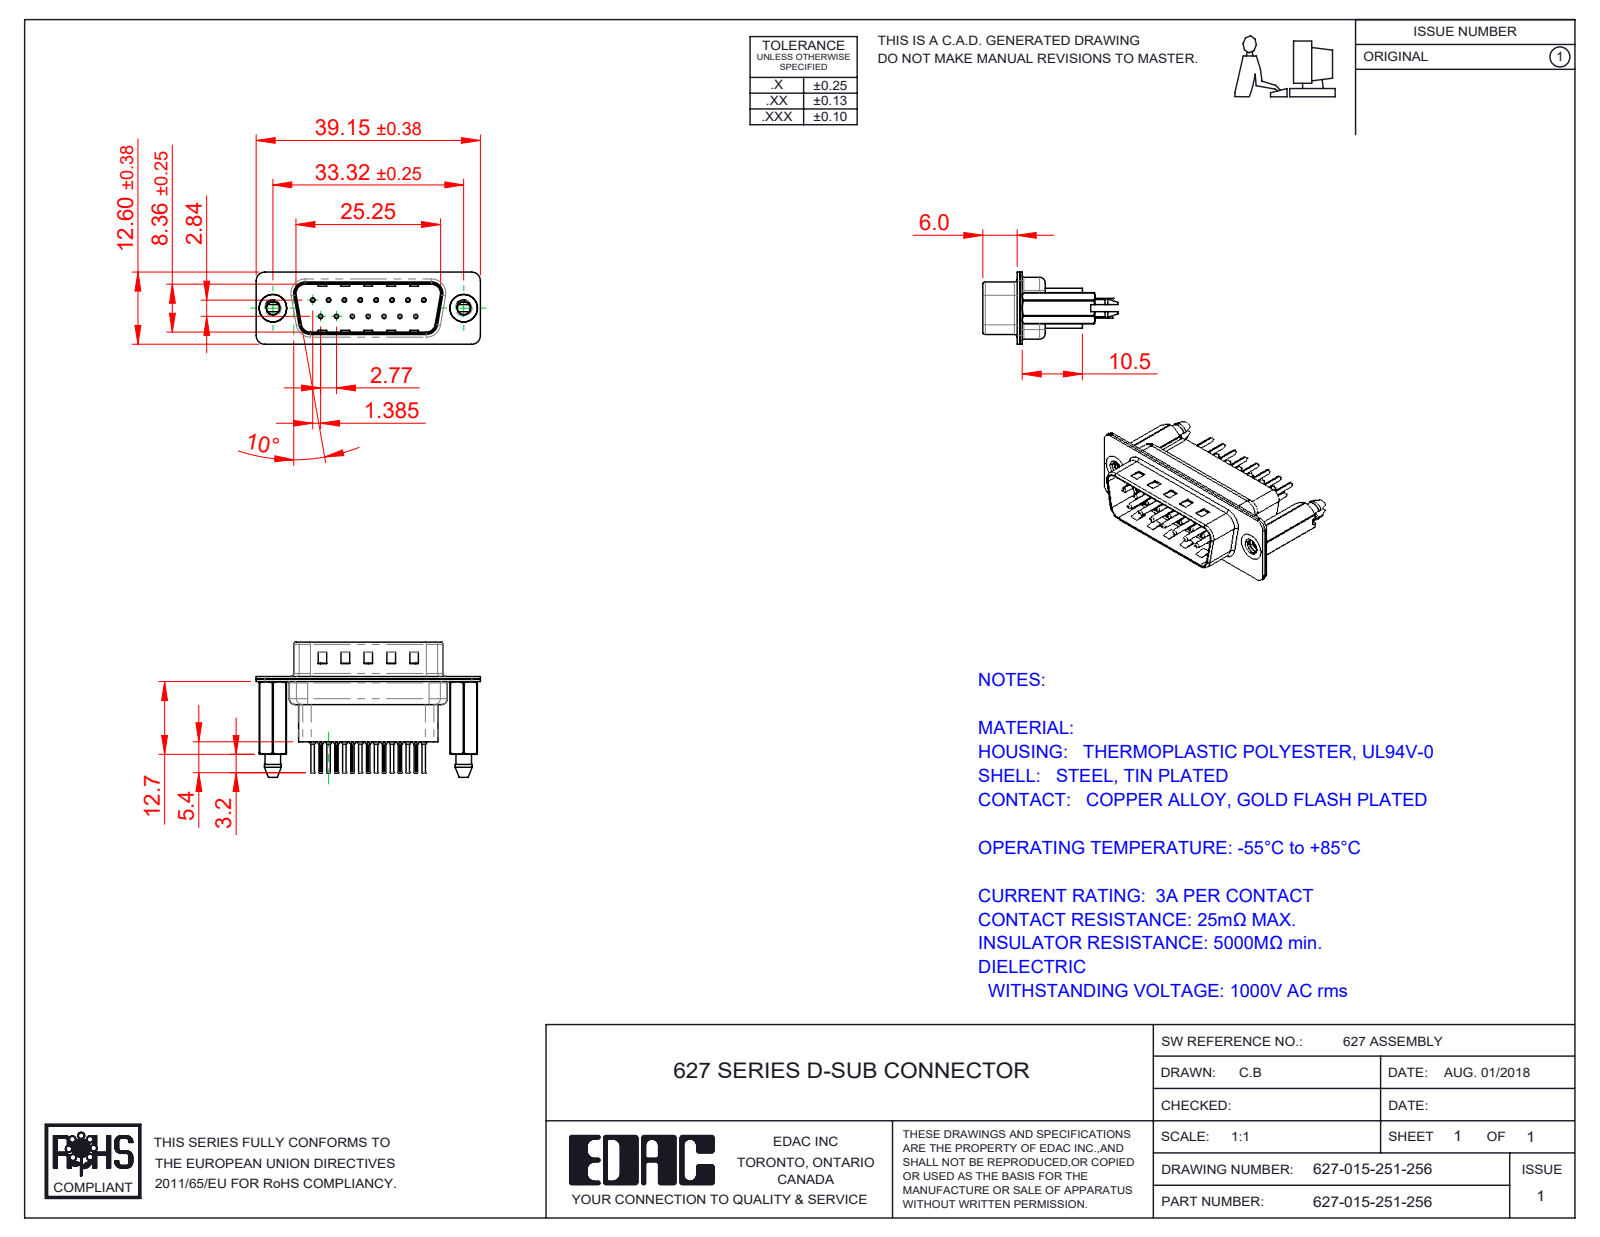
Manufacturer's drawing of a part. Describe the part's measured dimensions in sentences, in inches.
The part is named "627 Contact Row 1_41; 627 Shell Rear_15 Contacts; 627 Shell Front_15 Contacts; 627 Contact Row 2_41 (+3 more)". Its 3-D file was written by "SolidWorks 2020 (CONFIG_CONTROL_DESIGN)". It is 20 solids with 1918 faces: 531 planar, 754 cylindrical and 633 other. Overall it measures 1.541 by 0.929 by 0.496 inches. Its volume is 0.174 cubic inches and its surface area 11.42 square inches. Round holes: 15 of diameter 0.008, 15 of diameter 0.014, 15 of diameter 0.043, 15 of diameter 0.063, 2 of diameter 0.089, 2 of diameter 0.157, 2 of diameter 0.189. Round bosses or shafts: 15 of diameter 0.079, 15 of diameter 0.059, 15 of diameter 0.03, 15 of diameter 0.024, 2 of diameter 0.193. Partial cylindrical surfaces (rounded edges, fillets, slot ends): 30 of radius 0.004, 18 of radius 0.059, 12 of radius 0.079, 10 of radius 0.063, 8 of radius 0.02, 4 of radius 0.01, 4 of radius 0.024, 4 of radius 0.026. The main face-to-face distances are 0.016, 0.018, 0.035, 0.032, 0.377, 0.059, 0.027, 0.302, 0.187, 0.055. The hole center spacings are 0.124, 0.109, 0.218, 0.327, 0.436, 0.198, 0.198, 0.294.
